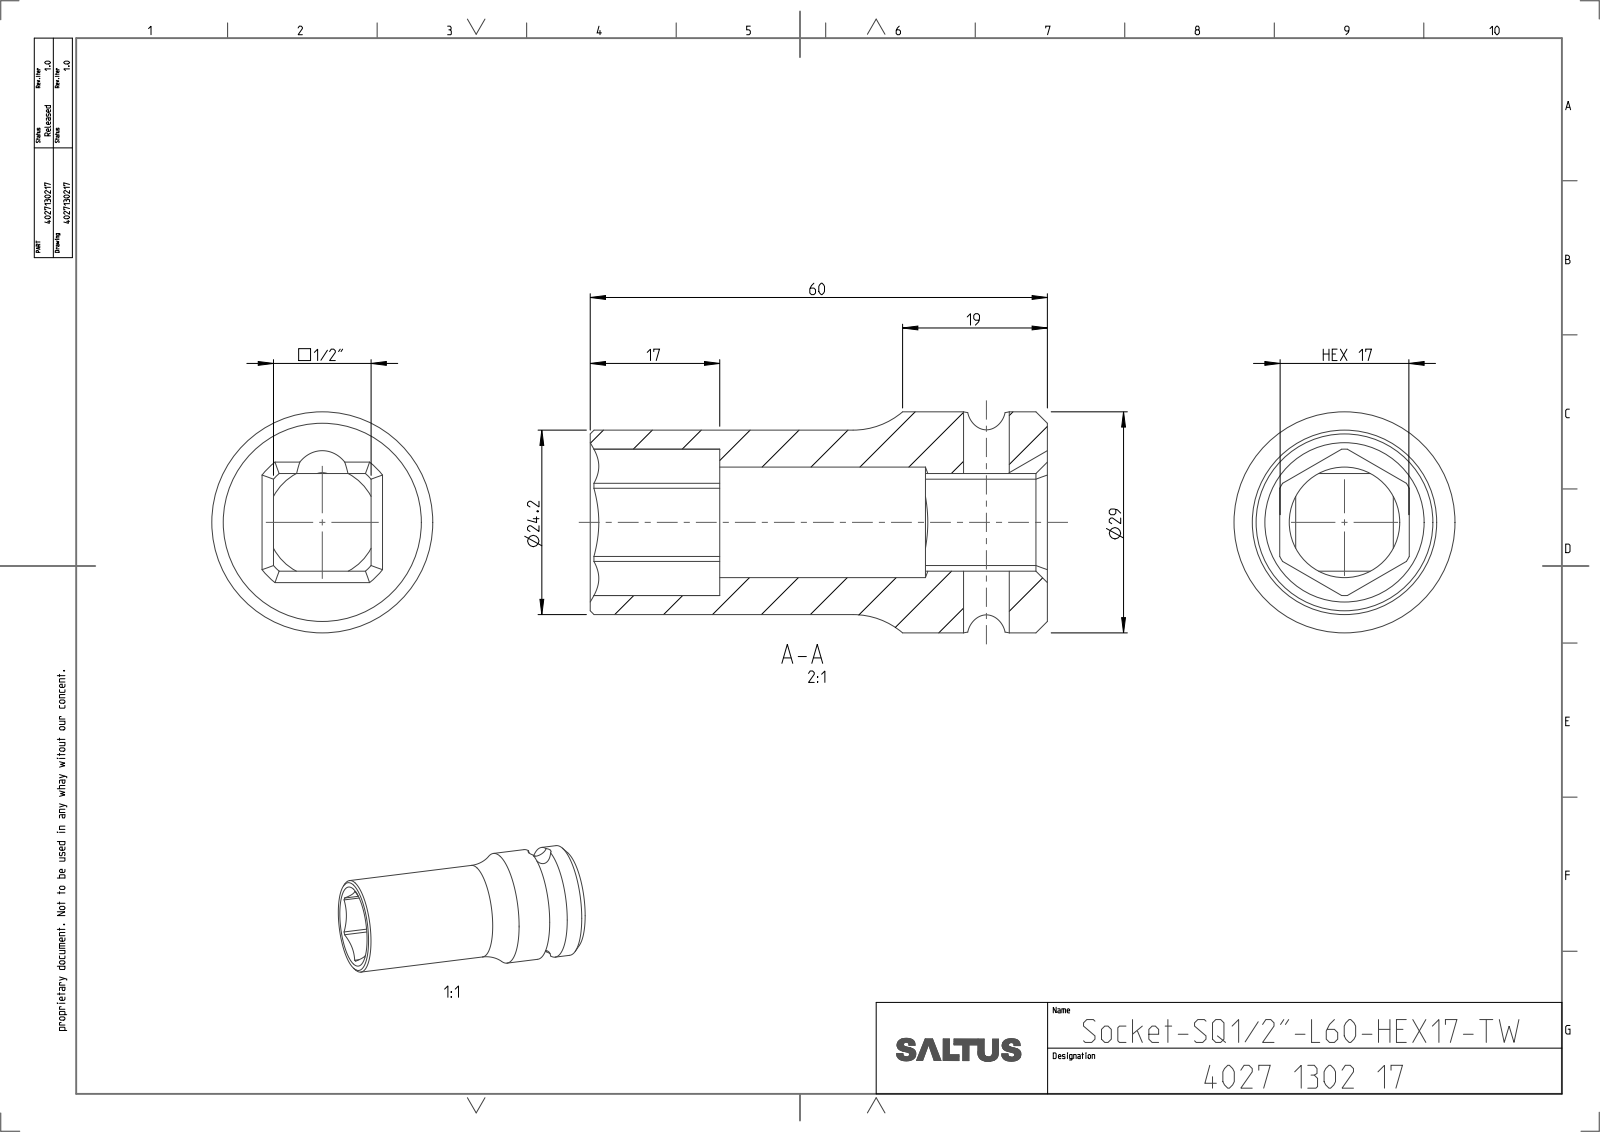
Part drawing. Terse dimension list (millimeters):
name: 4027130217
written by: CREO PARAMETRIC BY PTC INC, 2022414 (CONFIG_CONTROL_DESIGN)
unit: mm
bodies: 1 solid, 63 faces (22 planar, 23 cylindrical, 18 other)
size: 60 × 29 × 29
volume: 19 249 mm³; area: 8 829 mm²
holes: 1× ⌀6, 1× ⌀14.5
bosses: 1× ⌀29, 1× ⌀24.2
rounds: 1× R4, 1× R8.55, 1× R9.61
face distances: 17, 2.09, 14.91, 12.82, 43, 60, 16, 27, 44
